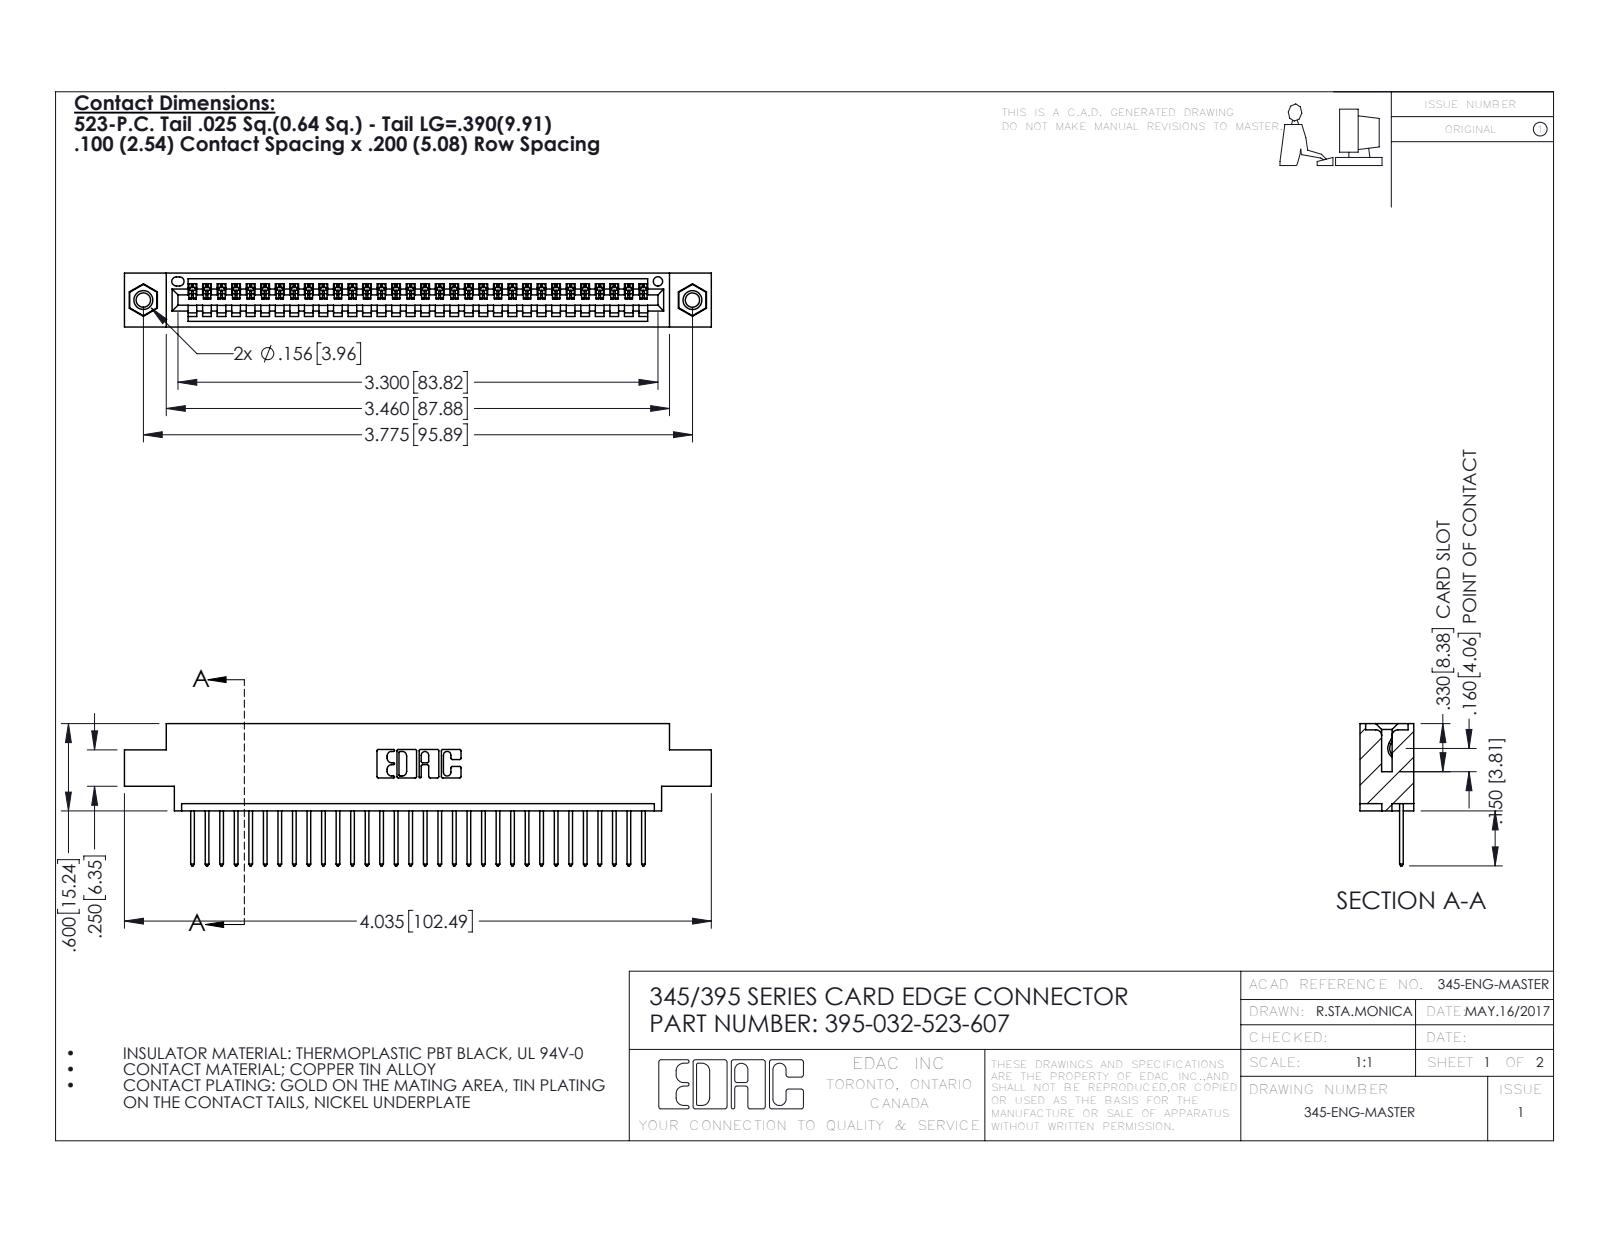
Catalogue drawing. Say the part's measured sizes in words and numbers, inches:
The part is named "395-032-523-607; 345 Part_0.170 Offset - 0.156 Dia-TI; 345-250-001_345-250-005-103; 345-292-001_345-293-123". Its 3-D file was written by "SolidWorks 2016 (CONFIG_CONTROL_DESIGN)". It is 35 solids with 2046 faces: 1396 planar, 634 cylindrical and 16 other. Overall it measures 4.035 by 0.977 by 0.37 inches. Its volume is 0.581 cubic inches and its surface area 19.69 square inches. Round holes: 2 of diameter 0.098, 2 of diameter 0.125, 2 of diameter 0.156, 1 of diameter 0.064. Round bosses or shafts: 2 of diameter 0.155. Partial cylindrical surfaces (rounded edges, fillets, slot ends): 64 of radius 0.006, 64 of radius 0.01, 22 of radius 0.01, 6 of radius 0.007, 6 of radius 0.031, 3 of radius 0.026, 2 of radius 0.031, 2 of radius 0.04. The main face-to-face distances are 0.072, 0.298, 0.37, 0.2, 0.098, 0.272, 0.025, 0.225, 0.175, 0.149. The hole center spacings are 0.27, 3.54, 3.775.
